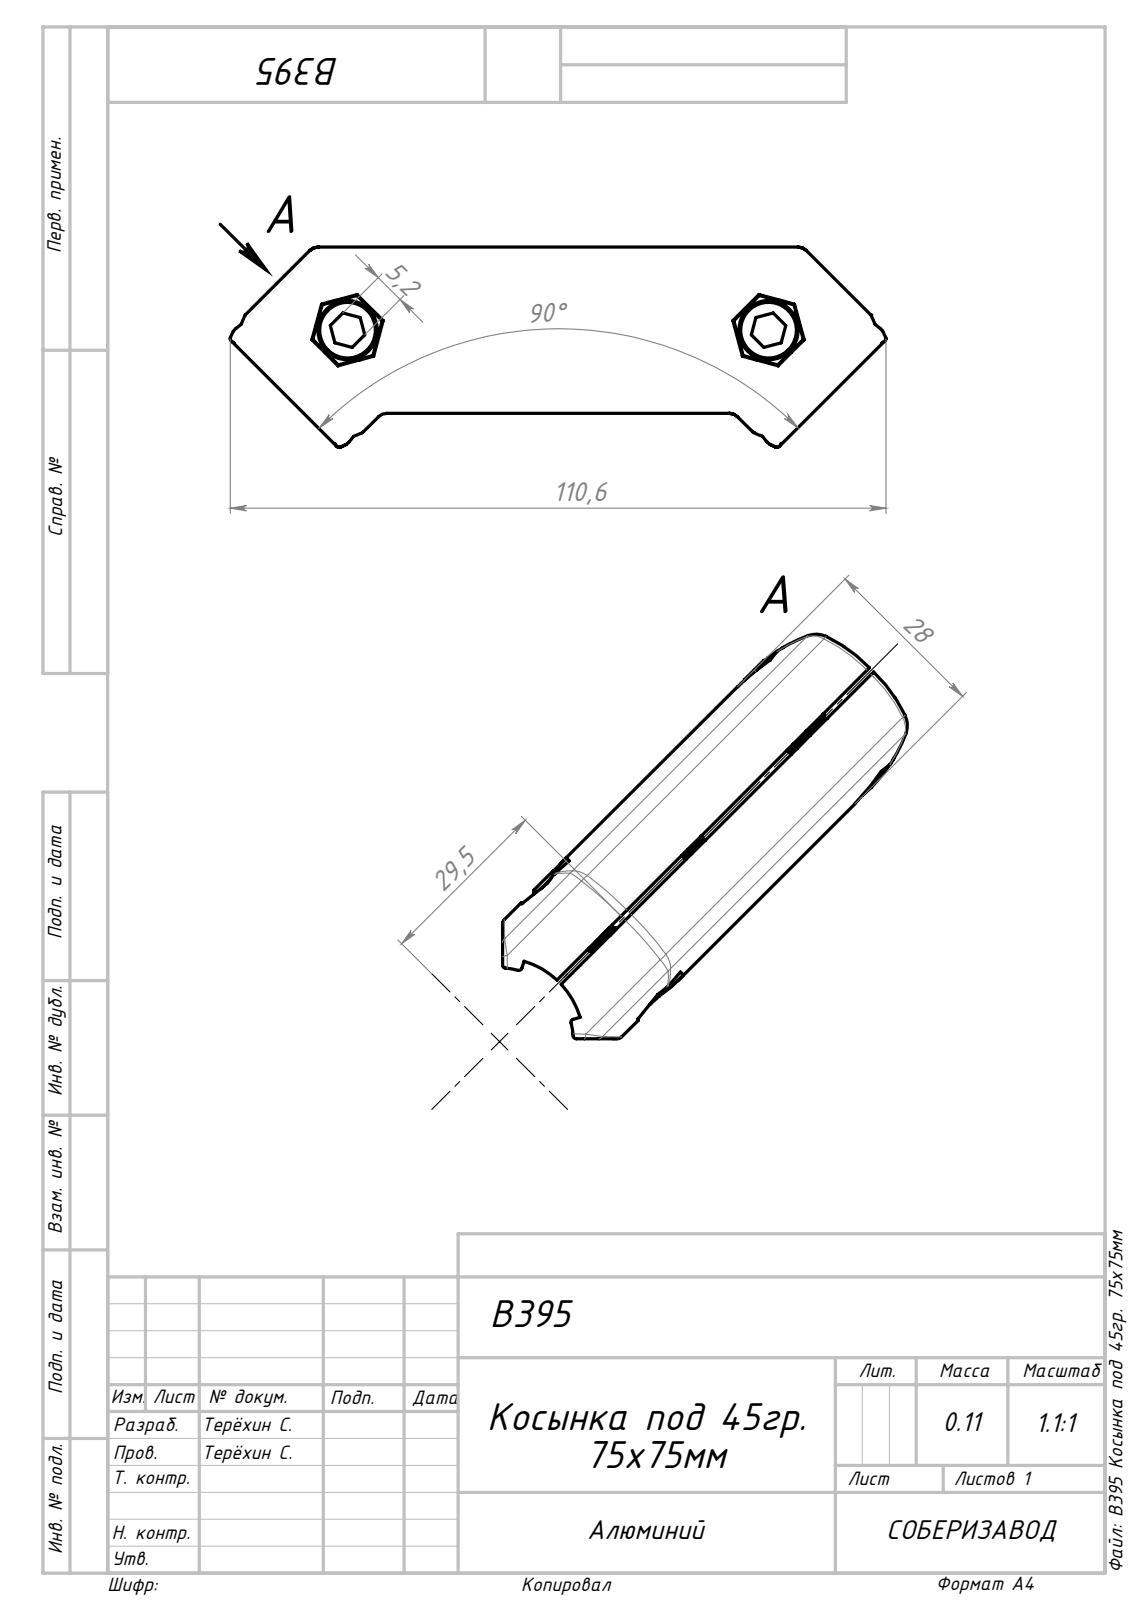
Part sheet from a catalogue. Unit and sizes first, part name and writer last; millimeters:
Units: millimetres
Overall size (bounding box): 110.58 × 33.81 × 28
Round holes (diameter × count): ⌀5.2 ×2, ⌀6.5 ×2
Round bosses / shafts (diameter × count): ⌀10 ×2, ⌀6 ×2
Partial cylindrical surfaces — rounded edges, fillets, slot ends (radius × count): R0.5 ×20, R25 ×18, R4 ×12, R22.5 ×10, R12.45 ×2, R14.2 ×2
Main face-to-face distances: 1, 2.46, 5.5, 23.26, 25.72, 4.5, 10, 6.5, 11, 48.98
Hole centre spacings: 71
Volume: 41 357 mm³ · Surface area: 25 674 mm²
Bodies: 6 solids, 490 faces (134 planar, 196 cylindrical, 160 other)
Part name (STEP PRODUCT): B395 Косынка под 45гр. 75х75мм
STEP written by: SolidWorks 2022 (AUTOMOTIVE_DESIGN)
